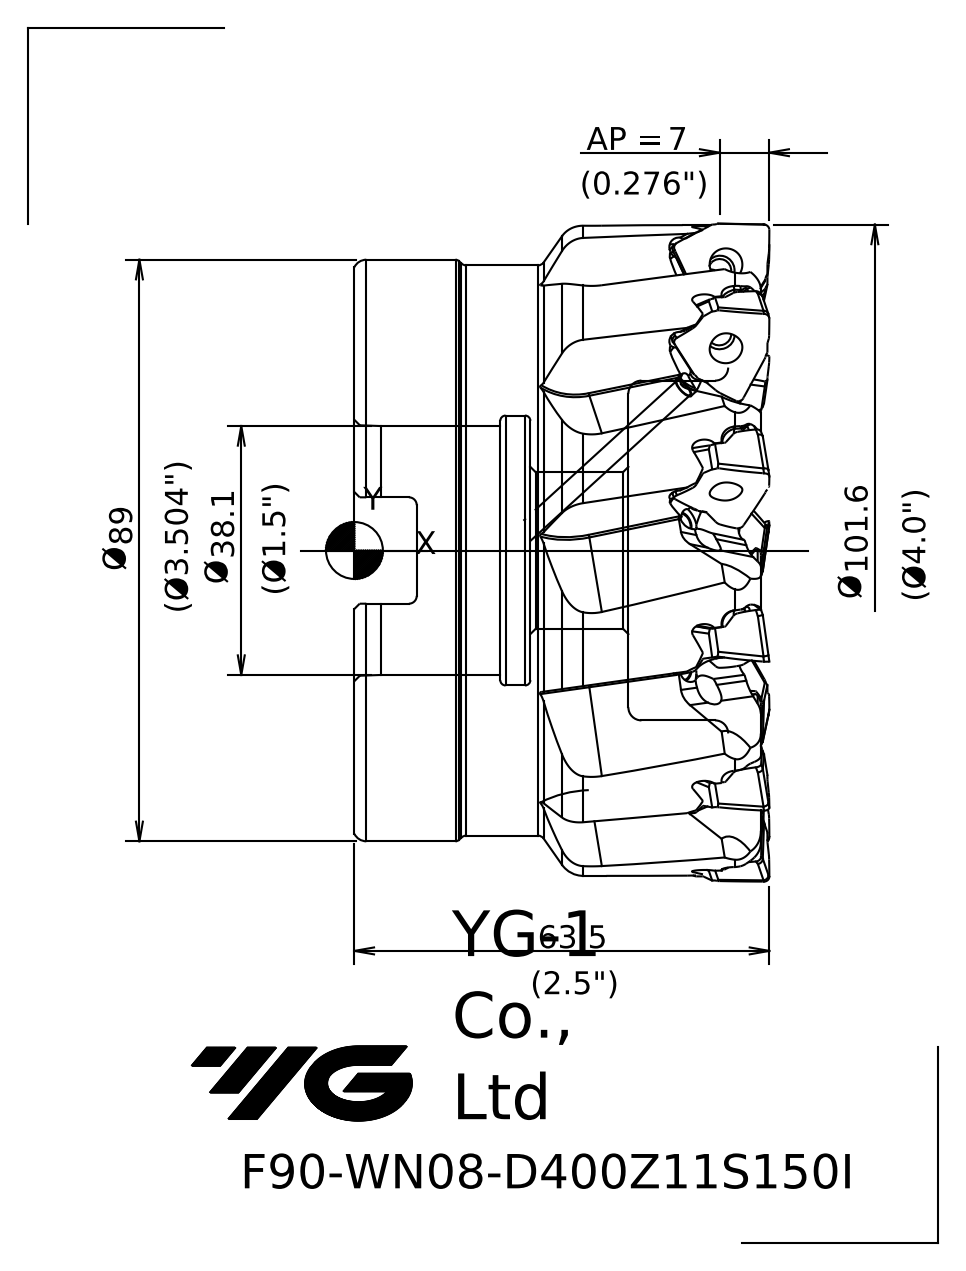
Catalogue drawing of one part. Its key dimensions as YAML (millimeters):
part_name: "10226A983EDD4gcr"
step_written_by: "SIEMENS PLM Software NX 10.0 (AP203_CONFIGURATION_CONTROLLED_3D_DESIGN_OF_MECHANICAL_PARTS_AND_ASSEMBLIES_MIM_LF)"
units: millimeters
bodies: {solids: 1, faces: 90, planar: 17, cylindrical: 11, other: 62}
overall_size: [101.62, 101.62, 63.5]
volume: 330371
surface_area: 51436
round_holes:
  - {diameter: 24, count: 1}
  - {diameter: 38.1, count: 1}
  - {diameter: 41.3, count: 1}
  - {diameter: 52, count: 1}
round_bosses_or_shafts:
  - {diameter: 99.6, count: 1}
  - {diameter: 89, count: 1}
  - {diameter: 87.3, count: 1}
partial_cylinders:
  - {radius: 1.2, count: 2}
face_to_face_distances: [41.92, 20.28, 62.2, 5, 15.28, 57.2, 35.28, 30.28, 15, 26.92]
